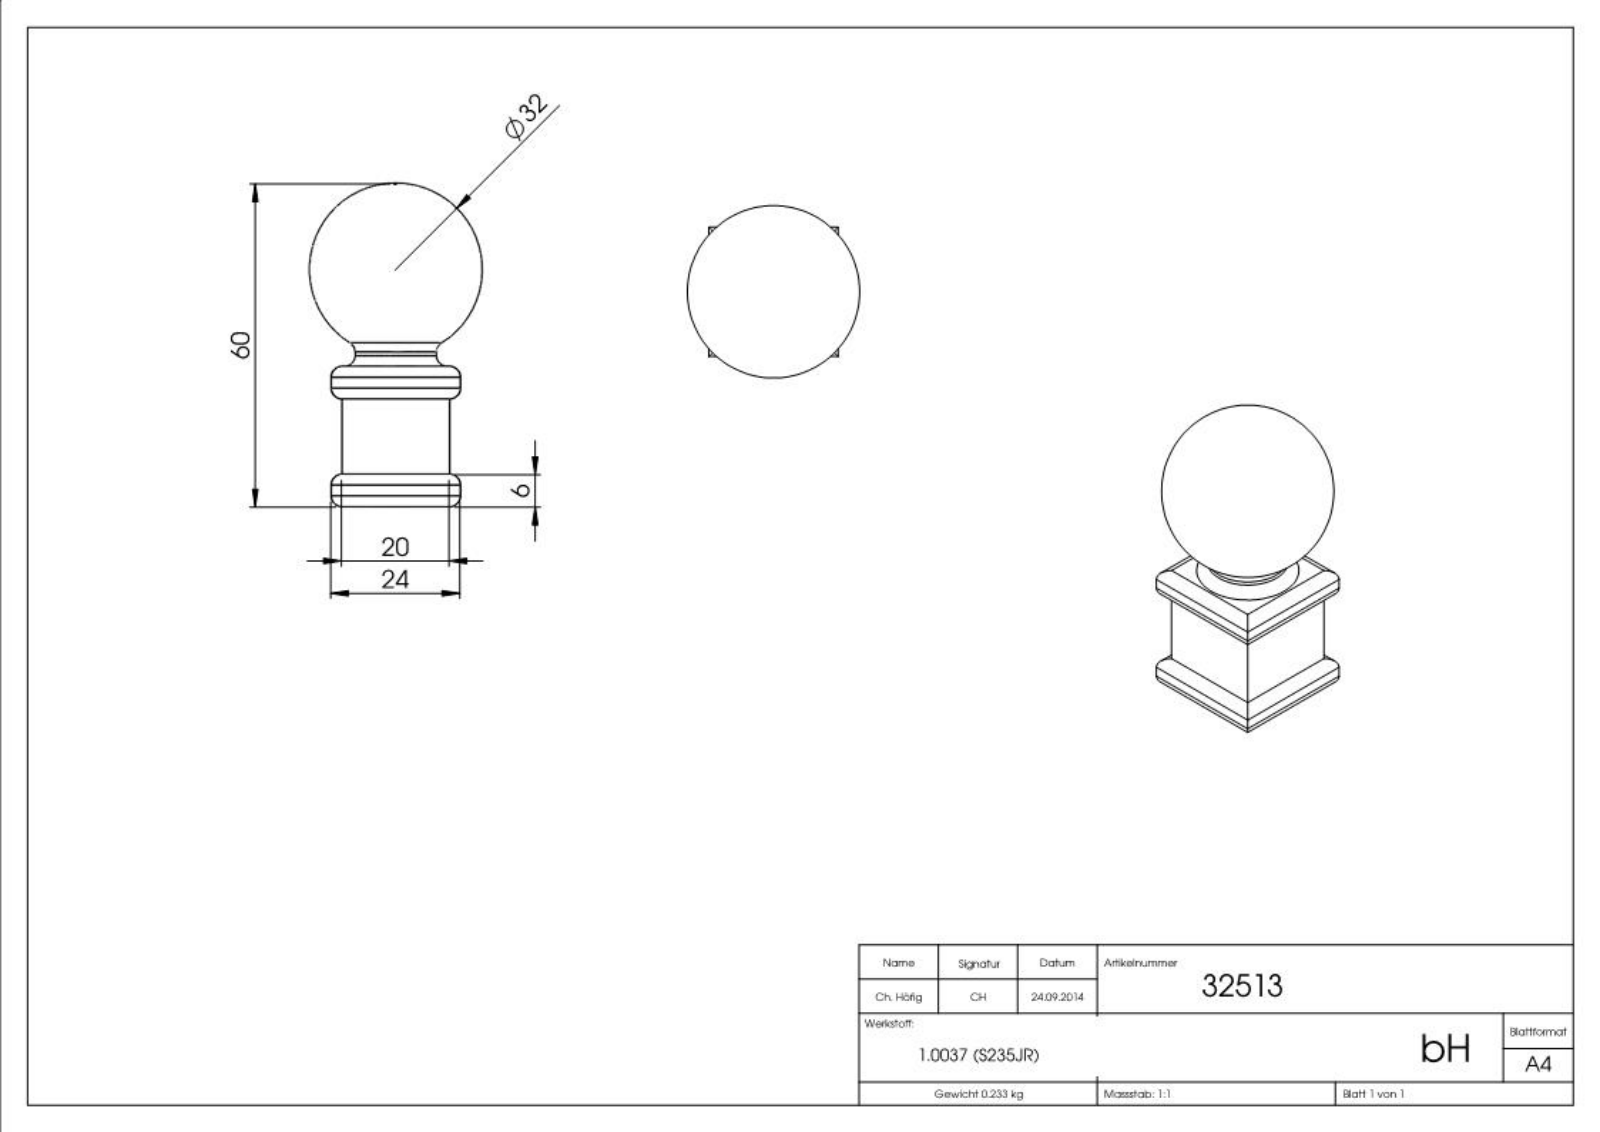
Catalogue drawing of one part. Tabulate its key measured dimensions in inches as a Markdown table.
| quantity | value |
| --- | --- |
| part name | 32513 |
| STEP written by | SolidWorks 2015 (CONFIG_CONTROL_DESIGN) |
| units | inches |
| bodies | 1 solid, 222 faces (108 planar, 18 cylindrical, 96 other) |
| overall size | 2.362 × 1.26 × 1.26 |
| volume | 1.826 in³ |
| surface area | 10.02 in² |
| round bosses / shafts (diameter × count) | 0.591 × 1 |
| partial cylindrical surfaces (radius × count) | 0.079 × 16 |
| main face-to-face distances | 0.787, 0.079, 0.866, 0.945, 1.024, 0.02, 1.004, 0.394, 0.472, 0.015 |
